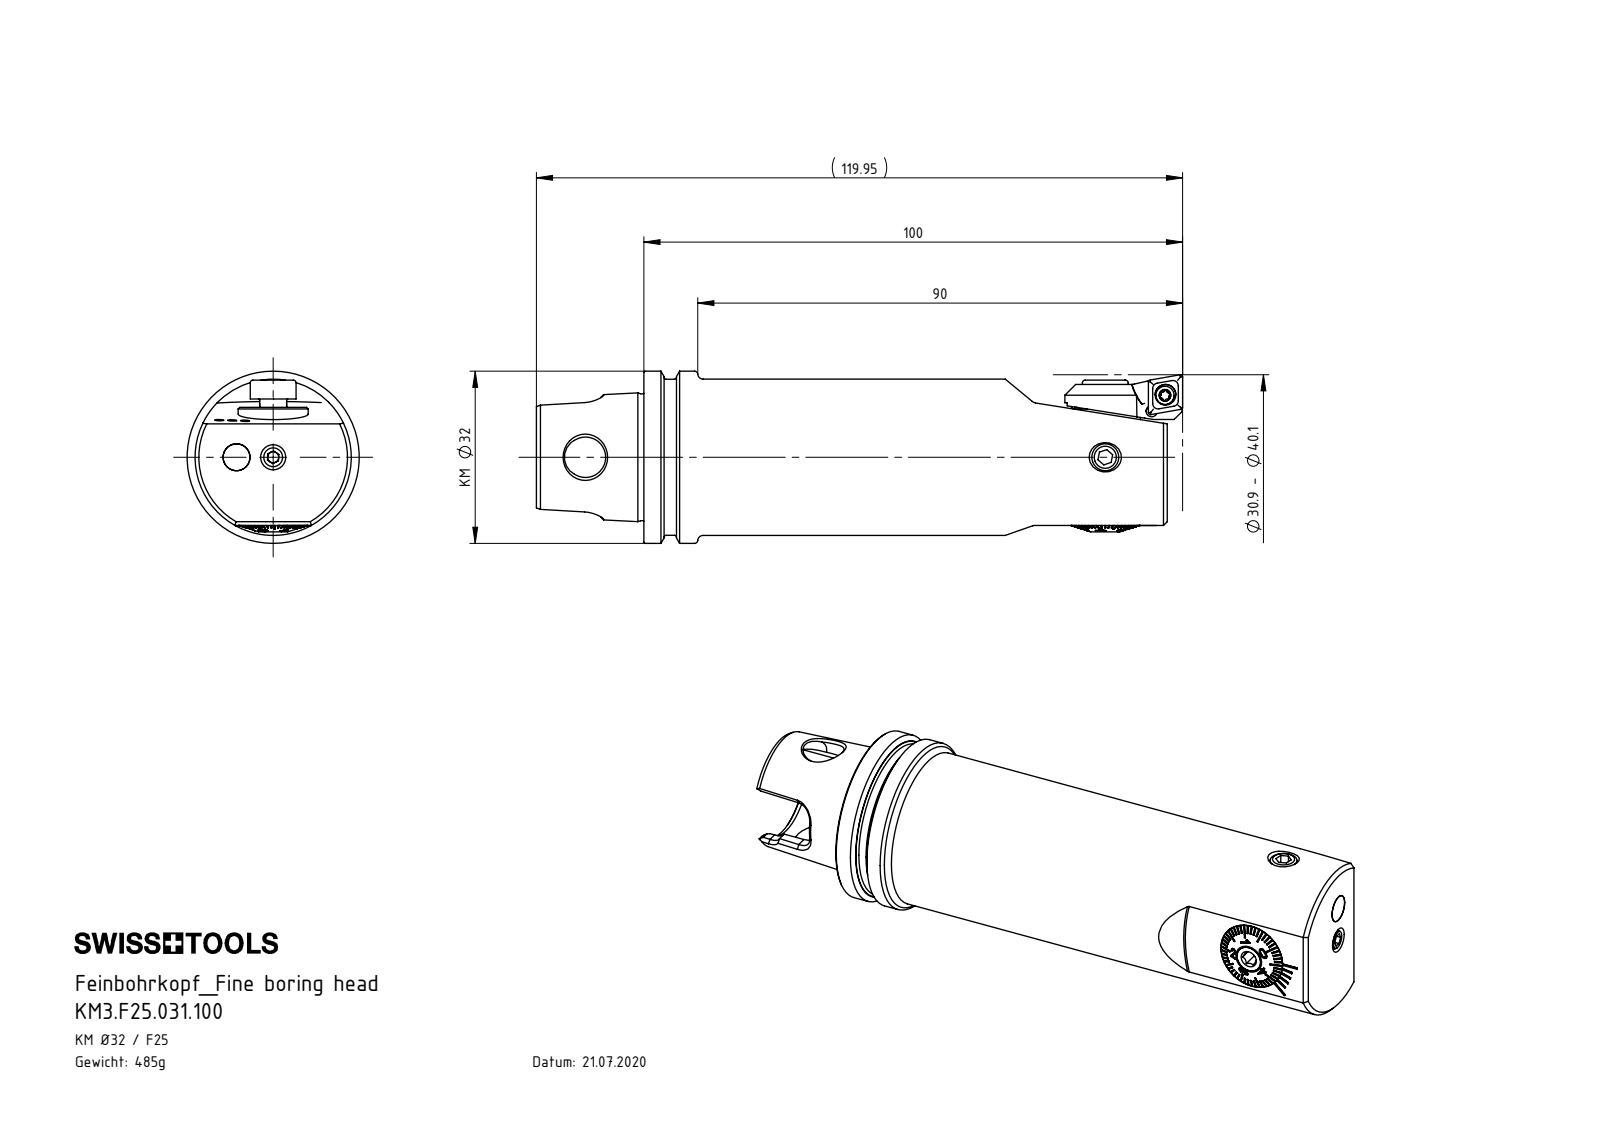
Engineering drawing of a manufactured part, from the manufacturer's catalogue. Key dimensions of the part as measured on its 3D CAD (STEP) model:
Part name (STEP PRODUCT): F25-BG1.009.006_A; KM3-F25.AA3.100_A_bohrungen gefllt; F25-BG1.DA4.013_Standardt; ISO 4026 - M5 x 6_PreviewCfg (+8 more)
STEP written by: SolidWorks 2017 (AUTOMOTIVE_DESIGN)
Units: millimetres
Bodies: 14 solids, 593 faces (327 planar, 74 cylindrical, 192 other)
Overall size (bounding box): 117.1 × 31.95 × 31.95
Volume: 62 105 mm³ · Surface area: 19 278 mm²
Round holes (diameter × count): ⌀1.5 ×3, ⌀2.5 ×2, ⌀4.2 ×2, ⌀2.05 ×1, ⌀2.4 ×1, ⌀2.7 ×1, ⌀3 ×1, ⌀3.3 ×1, ⌀5 ×1, ⌀5.5 ×1, ⌀6 ×1, ⌀6.4 ×1
Round bosses / shafts (diameter × count): ⌀5 ×2, ⌀4.95 ×2, ⌀31.95 ×1, ⌀29 ×1, ⌀28.95 ×1, ⌀13 ×1, ⌀12.98 ×1, ⌀12.85 ×1
Partial cylindrical surfaces — rounded edges, fillets, slot ends (radius × count): R1.4 ×4, R3 ×3, R0.5 ×2, R1.5 ×2, R3.54 ×2, R0.2 ×1, R1.25 ×1, R2 ×1
Main face-to-face distances: 1.5, 97.15, 3.91, 0.5, 2.5, 96.65, 3.1, 0.81, 2, 1.6
Hole centre spacings: 6.8, 7.32
